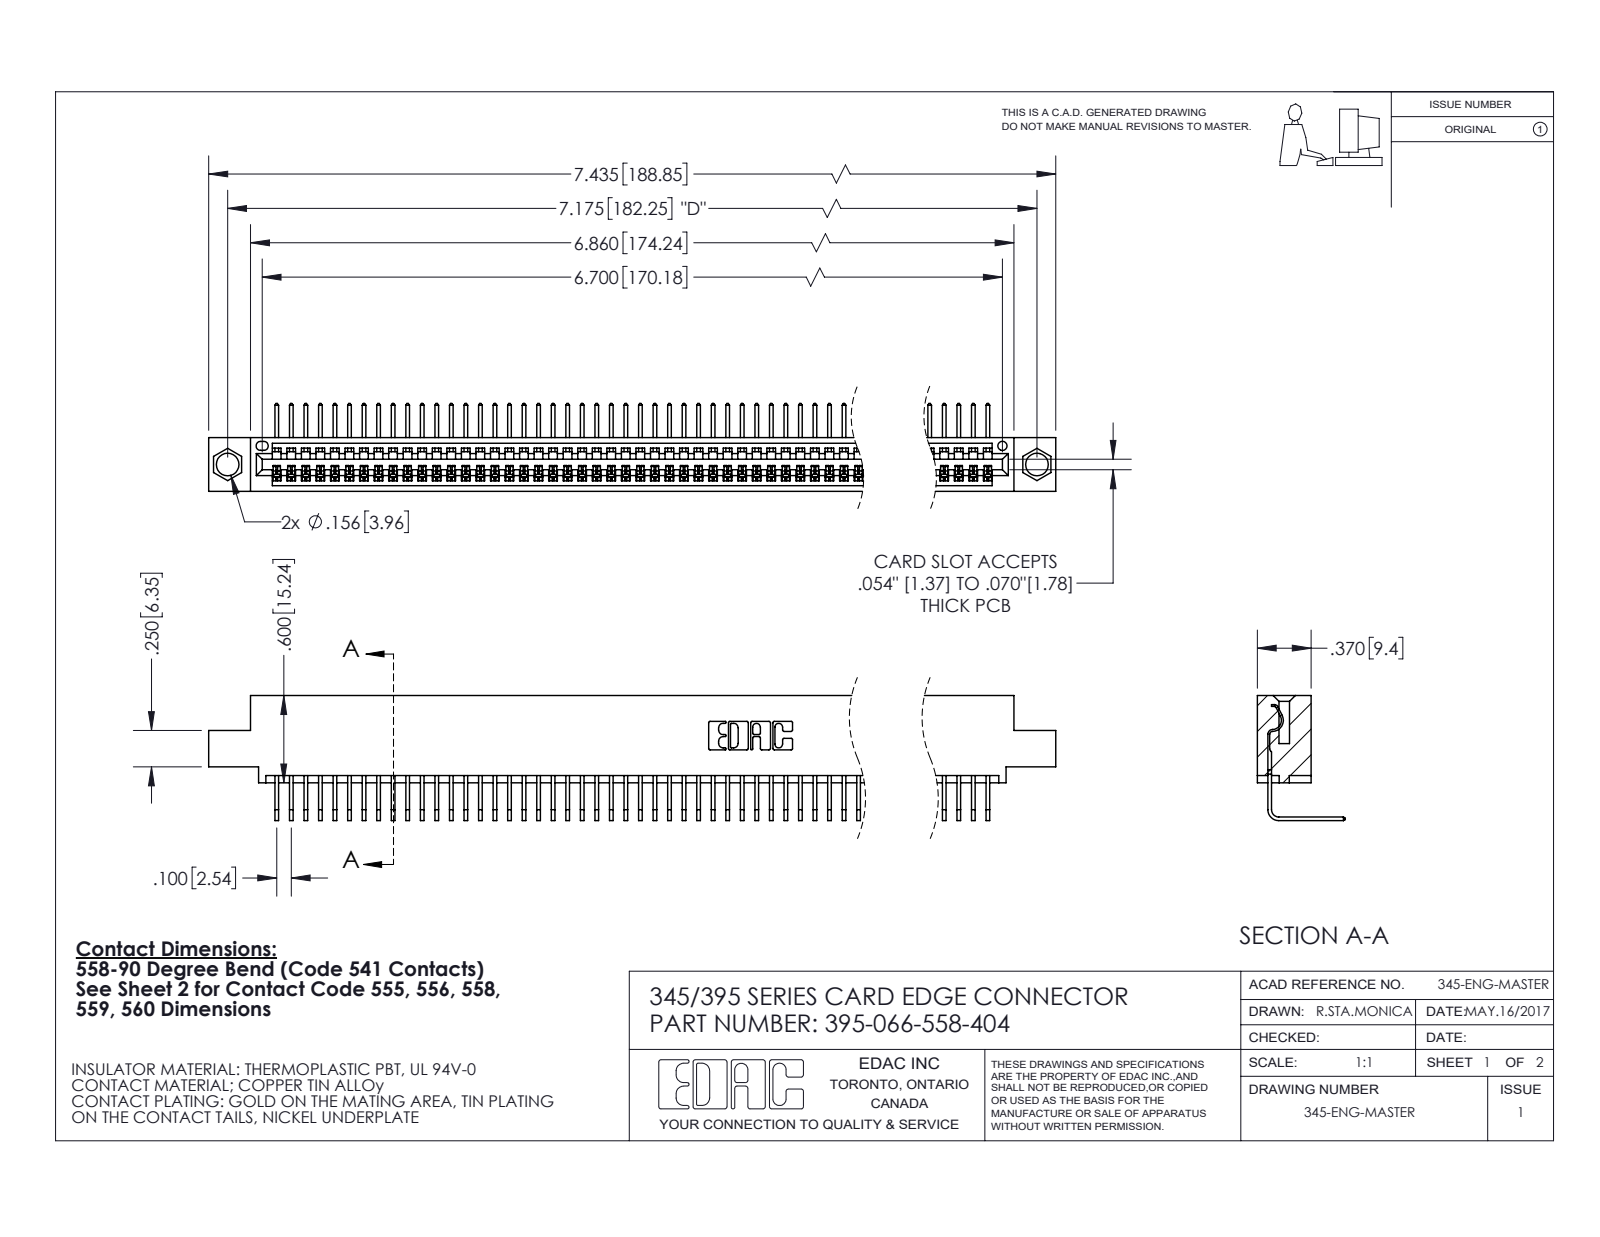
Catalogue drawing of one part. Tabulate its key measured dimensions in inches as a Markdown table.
| quantity | value |
| --- | --- |
| part name | 345 Part_0.110 Offset - 0.156 Dia-TI; 345-292-001_558 Tail - 2; 395-066-558-404 |
| STEP written by | SolidWorks 2020 (CONFIG_CONTROL_DESIGN) |
| units | inches |
| bodies | 67 solids, 4104 faces (2870 planar, 1234 cylindrical, 0 other) |
| overall size | 7.435 × 0.859 × 0.605 |
| volume | 1.109 in³ |
| surface area | 39.83 in² |
| round holes (diameter × count) | 0.156 × 2, 0.064 × 1 |
| partial cylindrical surfaces (radius × count) | 0.006 × 132, 0.01 × 22, 0.007 × 6, 0.031 × 6, 0.026 × 3, 0.031 × 2, 0.04 × 2, 0.014 × 1 |
| main face-to-face distances | 0.072, 0.298, 0.37, 0.2, 0.098, 0.272, 0.025, 0.225, 0.149, 0.072 |
| hole center spacings | 0.27, 6.939, 7.175 |
